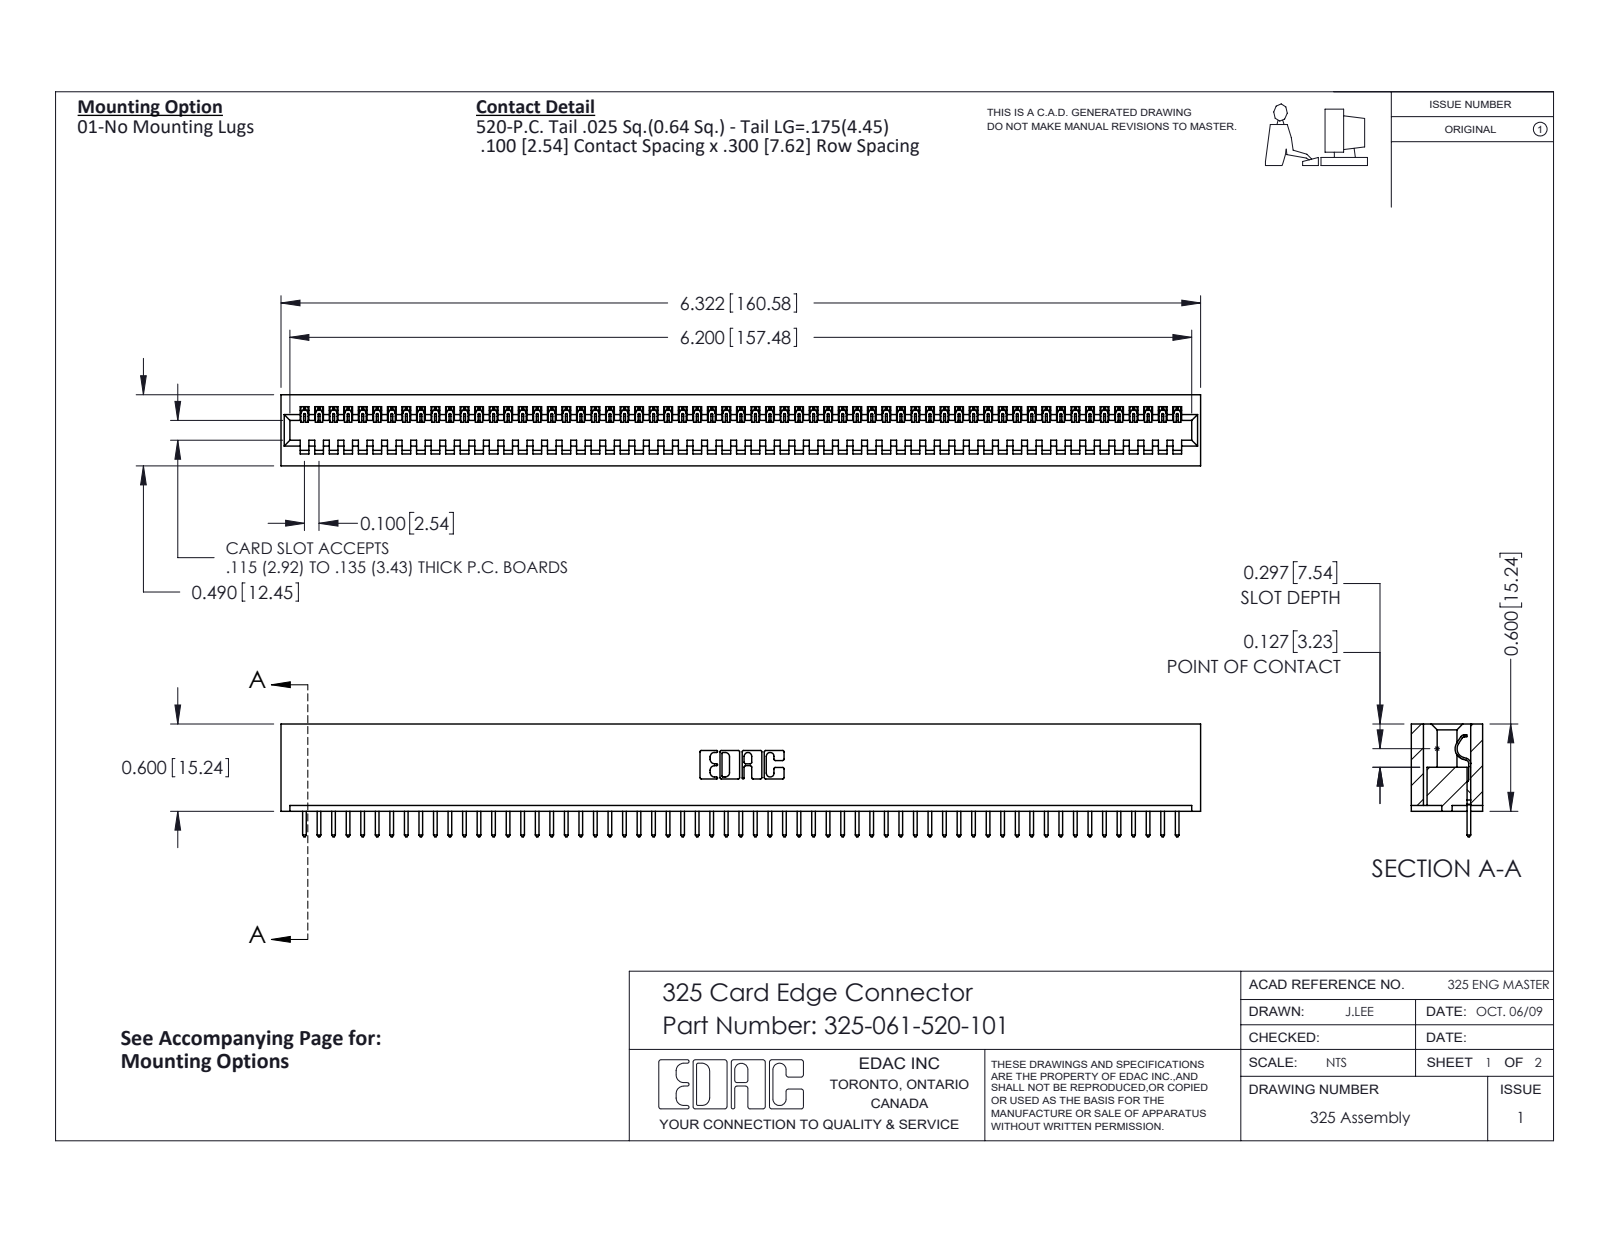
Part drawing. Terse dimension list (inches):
name: 325-061-520-101; 325-292-001_325-293-120; 325 Part_Lugless
written by: SolidWorks 2016 (CONFIG_CONTROL_DESIGN)
unit: in
bodies: 62 solids, 3644 faces (2628 planar, 1016 cylindrical, 0 other)
size: 6.322 × 0.775 × 0.49
volume: 1.278 in³; area: 35.74 in²
rounds: 122× R0.006, 122× R0.01, 22× R0.01, 6× R0.007, 6× R0.031, 3× R0.026, 1× R0.014, 1× R0.022
face distances: 0.083, 0.407, 0.49, 0.3, 0.107, 0.383, 0.025, 0.325, 0.263, 0.56
